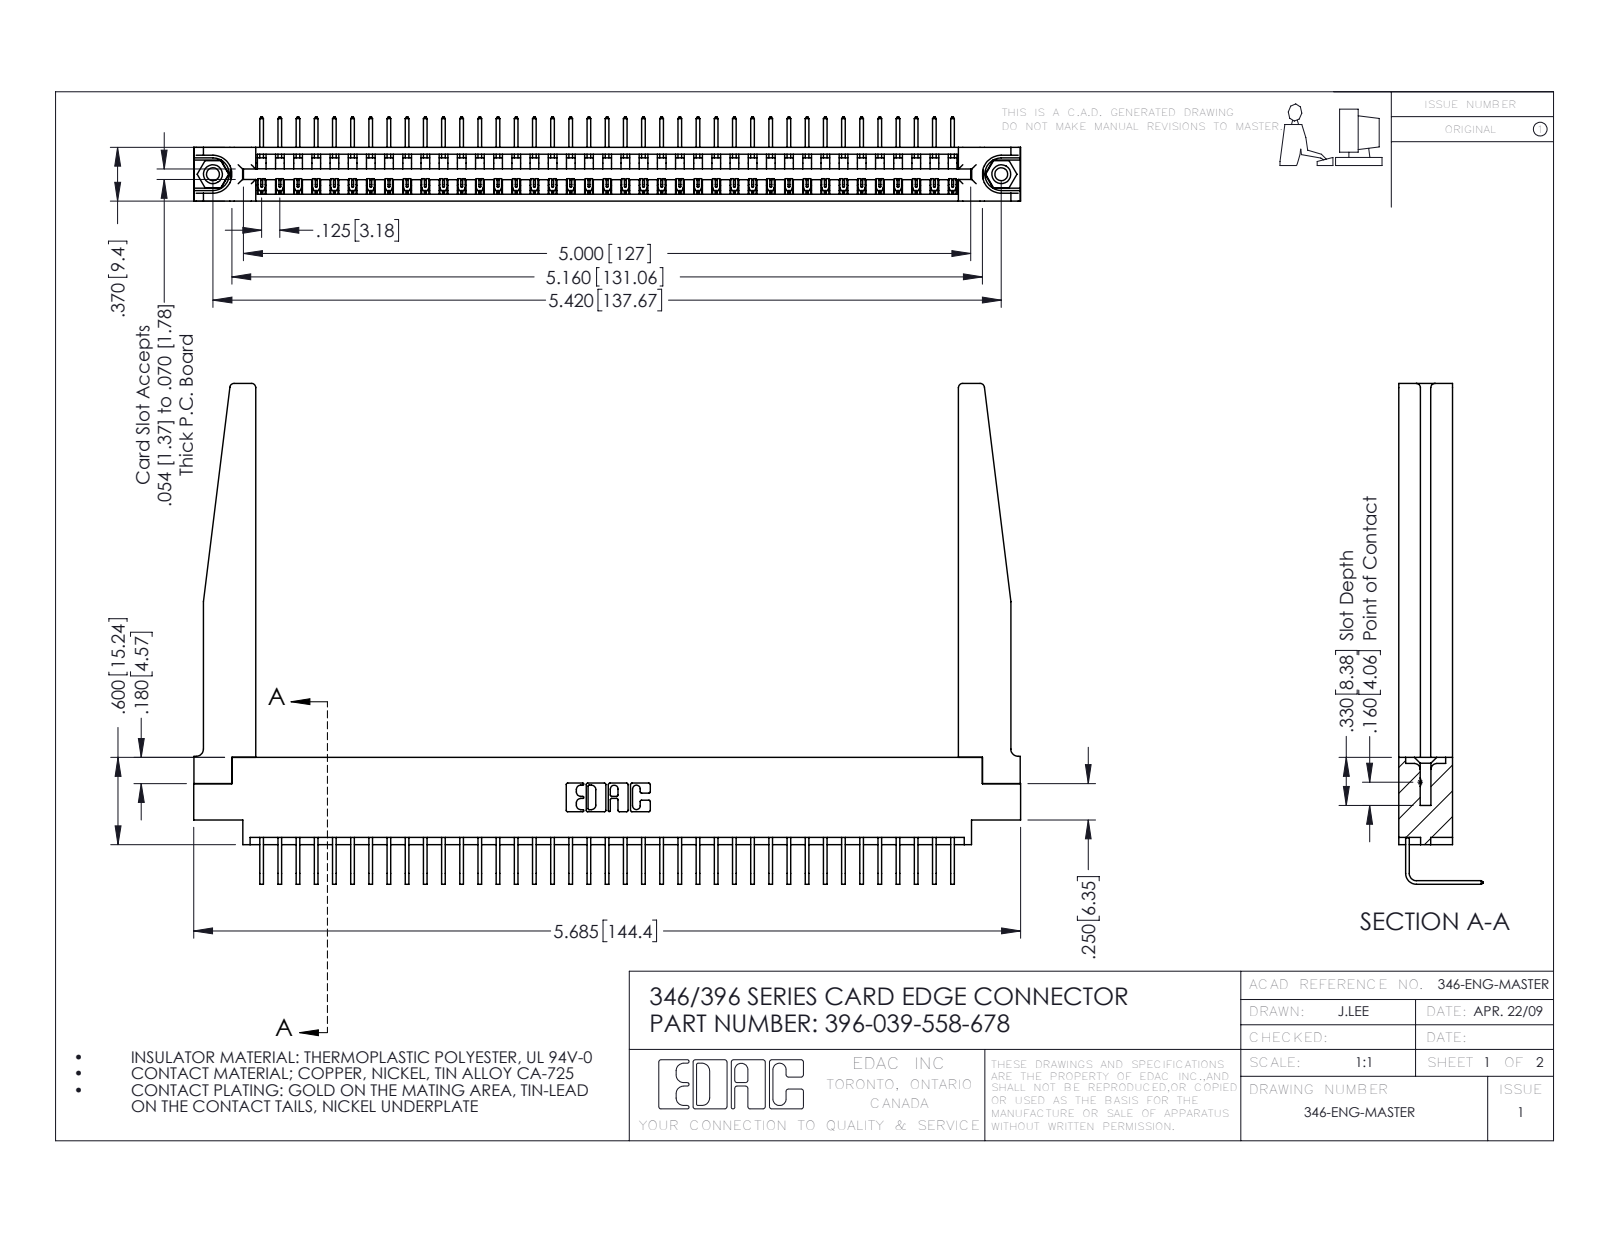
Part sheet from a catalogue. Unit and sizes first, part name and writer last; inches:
Units: inches
Overall size (bounding box): 5.685 × 3.443 × 0.58
Round holes (diameter × count): ⌀0.089 ×2, ⌀0.125 ×2, ⌀0.156 ×2, ⌀0.064 ×1
Round bosses / shafts (diameter × count): ⌀0.155 ×2
Partial cylindrical surfaces — rounded edges, fillets, slot ends (radius × count): R0.006 ×78, R0.01 ×22, R0.03 ×8, R0.007 ×6, R0.031 ×6, R0.026 ×3, R0.05 ×3, R0.031 ×2
Main face-to-face distances: 0.37, 0.322, 0.048, 0.072, 0.148, 0.15, 0.25, 0.298, 0.025, 0.222
Hole centre spacings: 0.246, 5.211, 5.42
Volume: 1.262 in³ · Surface area: 38.23 in²
Bodies: 44 solids, 2700 faces (1860 planar, 788 cylindrical, 52 other)
Part name (STEP PRODUCT): 346 Part_0.170 Offset - 0.156 Dia-TH; 396-039-558-678; 345-292-001_558 Tail - 2; 346-220-078_345-220-078 (+1 more)
STEP written by: SolidWorks 2016 (CONFIG_CONTROL_DESIGN)
